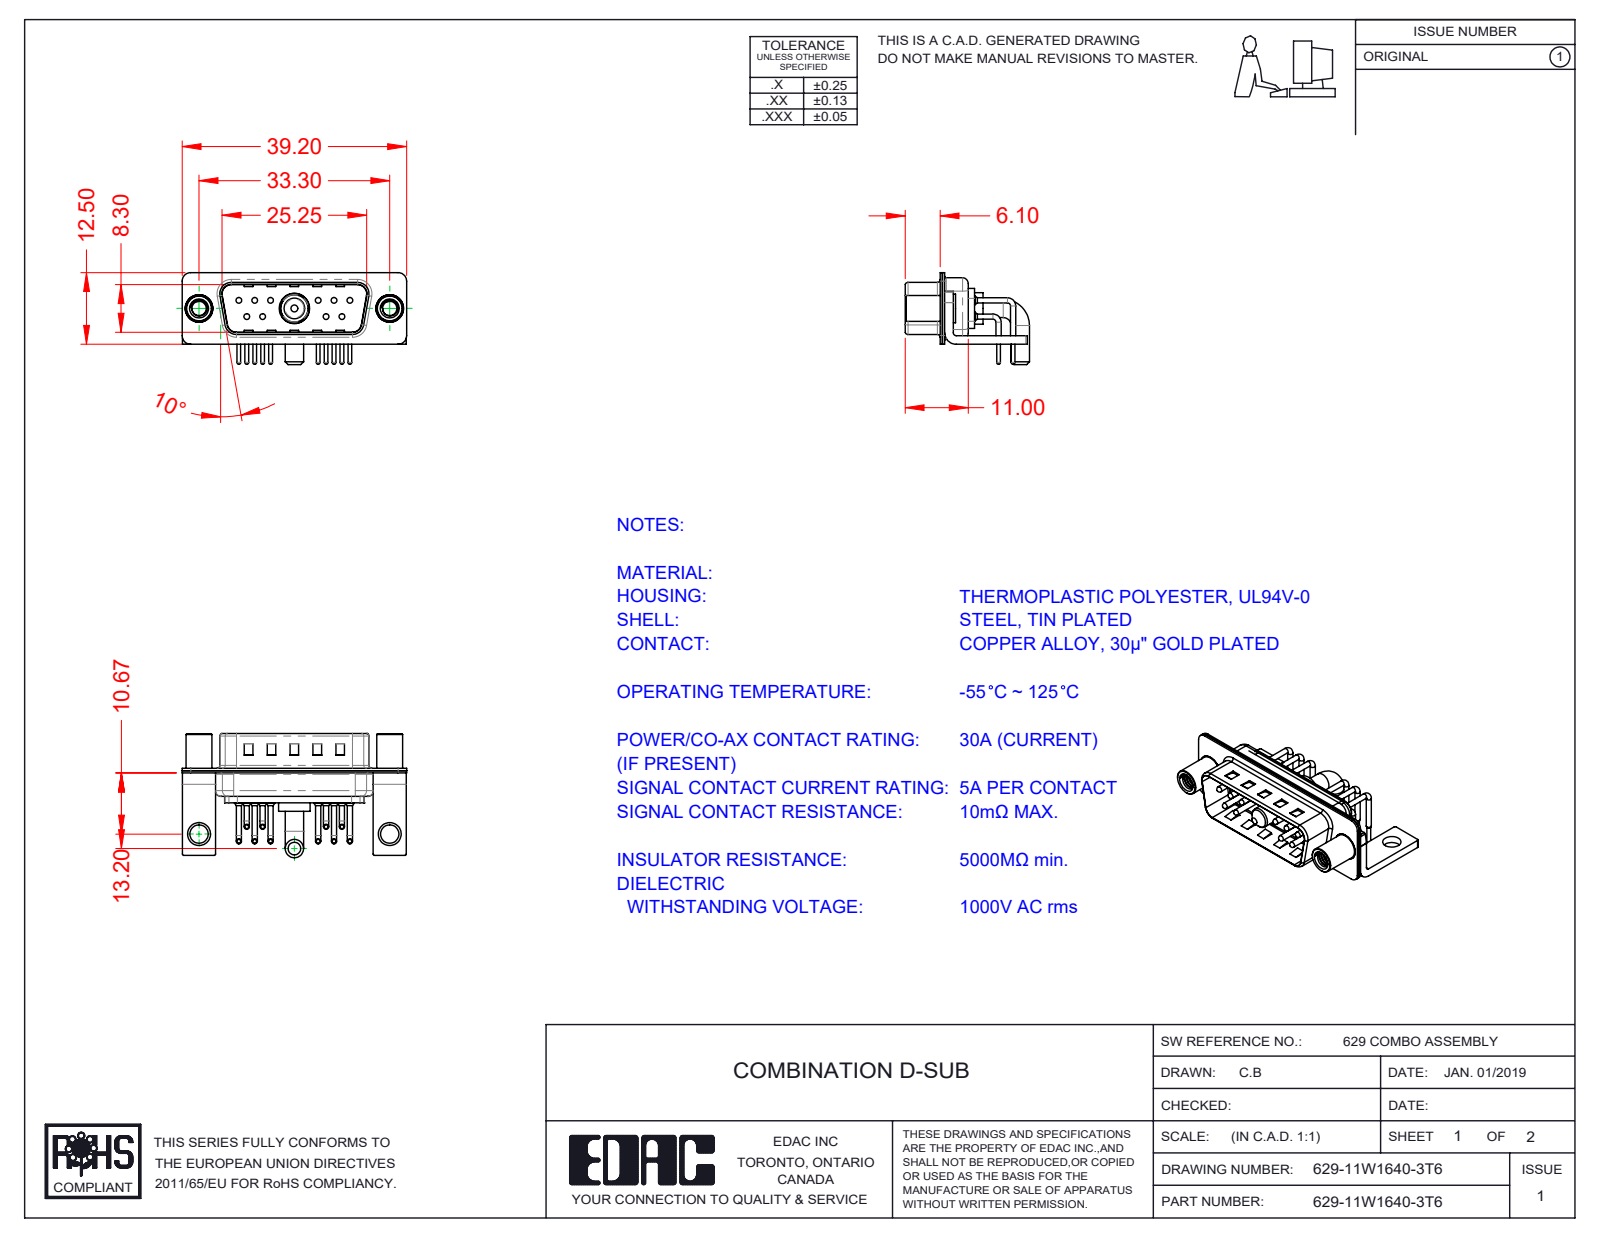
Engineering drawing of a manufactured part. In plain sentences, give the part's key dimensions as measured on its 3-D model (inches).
The part is named "629Combo Contact Row 2; 629-11W1640-3T6; 629Combo Housing_11W1; 629Combo Shell Front_15 Contacts (+5 more)". Its 3-D file was written by "SolidWorks 2020 (CONFIG_CONTROL_DESIGN)". It is 19 solids with 1594 faces: 820 planar, 590 cylindrical and 184 other. Overall it measures 1.543 by 0.854 by 0.632 inches. Its volume is 0.151 cubic inches and its surface area 9.573 square inches. Round holes: 10 of diameter 0.03, 10 of diameter 0.063, 10 of diameter 0.079, 2 of diameter 0.098, 2 of diameter 0.126, 2 of diameter 0.157, 2 of diameter 0.189, 1 of diameter 0.191, 1 of diameter 0.209. Round bosses or shafts: 20 of diameter 0.035, 10 of diameter 0.059, 10 of diameter 0.039, 10 of diameter 0.026, 2 of diameter 0.197, 2 of diameter 0.193, 2 of diameter 0.177, 2 of diameter 0.126. Partial cylindrical surfaces (rounded edges, fillets, slot ends): 16 of radius 0.01, 16 of radius 0.059, 13 of radius 0.079, 10 of radius 0.04, 9 of radius 0.02, 8 of radius 0.063, 7 of radius 0.039, 4 of radius 0.024. The main face-to-face distances are 0.016, 0.031, 0.059, 0.374, 0.358, 0.343, 0.39, 0.024, 0.075, 0.205. The hole center spacings are 0.124, 0.109, 0.545, 0.436, 0.654, 0.198, 0.198, 0.218.
